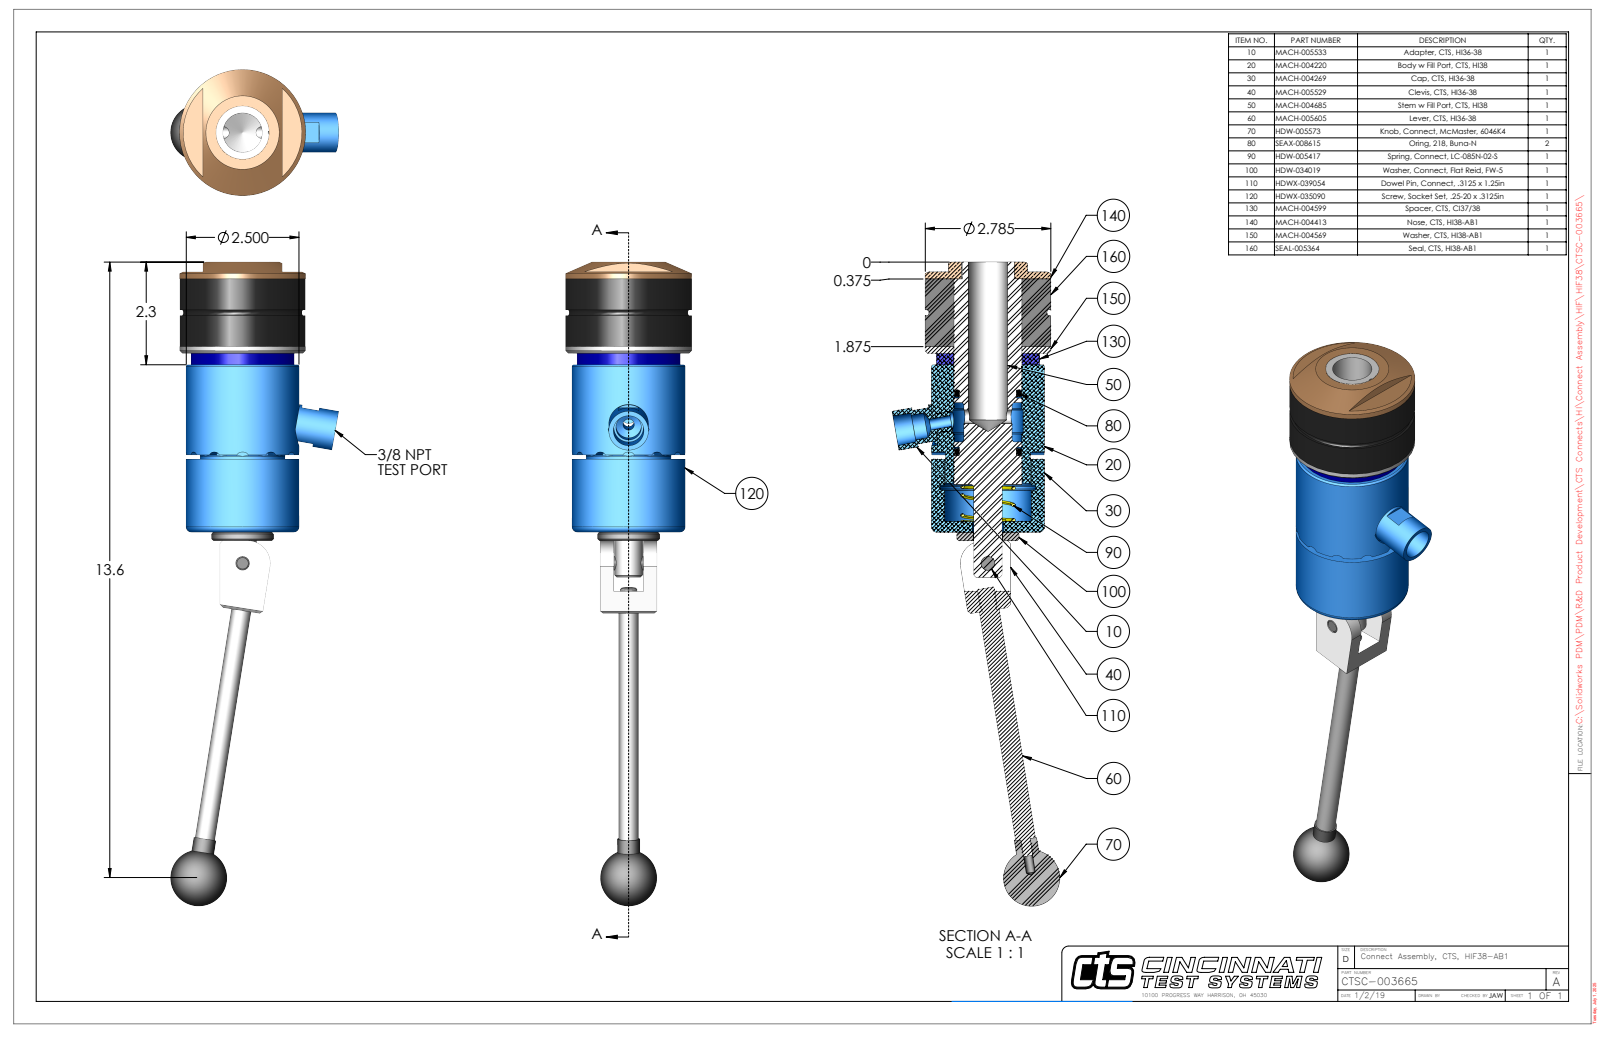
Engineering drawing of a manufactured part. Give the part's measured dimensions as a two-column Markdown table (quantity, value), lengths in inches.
| quantity | value |
| --- | --- |
| part name | CTSC-003665 |
| STEP written by | SolidWorks 2023 (AUTOMOTIVE_DESIGN) |
| units | inches |
| bodies | 10 solids, 316 faces (111 planar, 130 cylindrical, 75 other) |
| overall size | 14.275 × 3.716 × 2.785 |
| volume | 32.3 in³ |
| surface area | 160.7 in² |
| round holes (diameter × count) | 0.201 × 2, 0.15 × 1, 0.25 × 1, 0.311 × 1, 0.312 × 1, 0.313 × 1, 0.314 × 1, 0.562 × 1, 0.656 × 1, 0.696 × 1, 0.875 × 1, 1.172 × 1 |
| round bosses / shafts (diameter × count) | 2.785 × 1, 2.785 × 1, 2.5 × 1, 2.281 × 1, 1.875 × 1, 1.5 × 1, 1.498 × 1, 1.38 × 1 |
| partial cylindrical surfaces (radius × count) | 0.12 × 12, 0.029 × 2, 0.19 × 1, 0.195 × 1, 0.47 × 1, 0.474 × 1, 0.5 × 1, 1.201 × 1 |
| main face-to-face distances | 1.5, 0.152, 1.652, 0.25, 0.402, 1.902, 3.713, 3.963, 4.115, 5.615 |
| hole center spacings | 0.74, 2.118, 2.858 |
